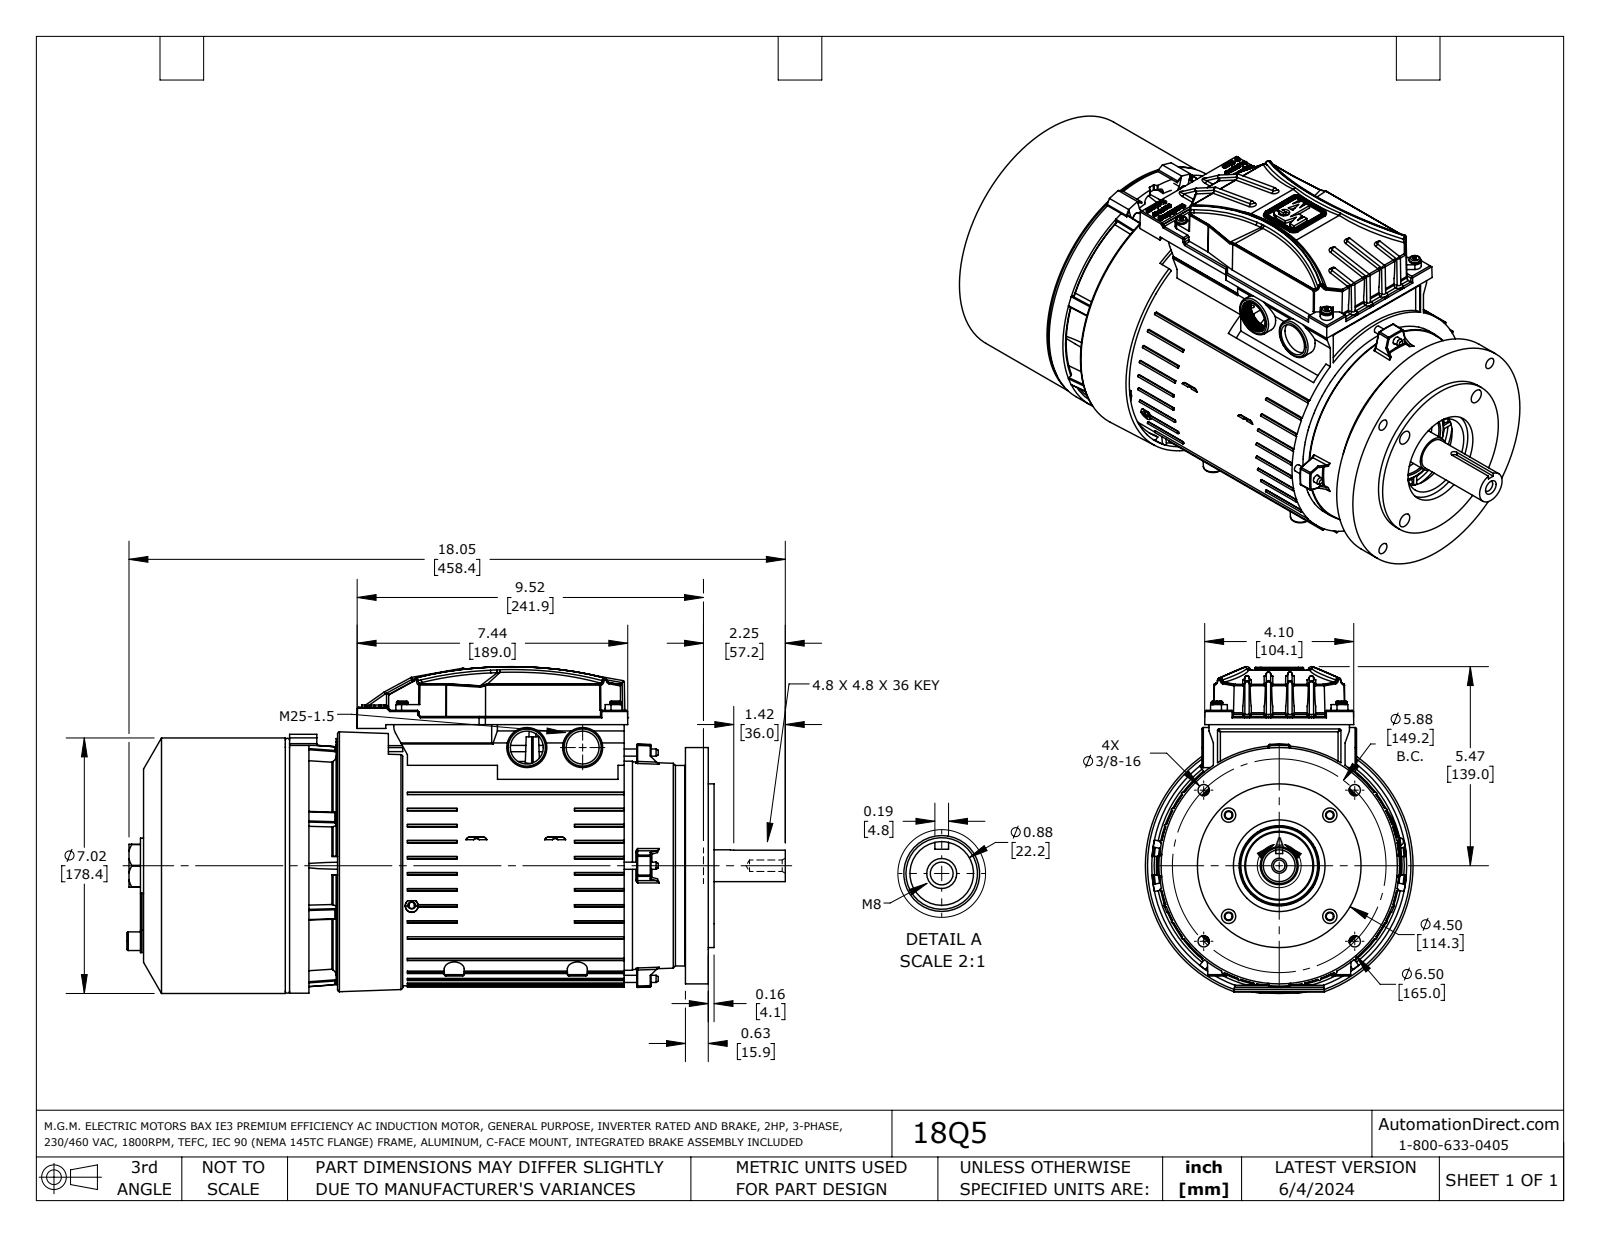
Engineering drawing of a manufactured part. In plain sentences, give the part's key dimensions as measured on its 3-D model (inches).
The part is named "18Q5". Its 3-D file was written by "SolidWorks 2021 (AUTOMOTIVE_DESIGN)". It is 14 solids with 3356 faces: 1425 planar, 768 cylindrical and 1163 other. Overall it measures 18.107 by 8.985 by 7.361 inches. Its volume is 506.6 cubic inches and its surface area 1 038 square inches. Round holes: 14 of diameter 0.13, 5 of diameter 0.098, 5 of diameter 0.236, 5 of diameter 0.315, 4 of diameter 0.15, 4 of diameter 0.177, 4 of diameter 0.197, 4 of diameter 0.313, 4 of diameter 0.394, 2 of diameter 0.118, 2 of diameter 0.906, 1 of diameter 0.276. Round bosses or shafts: 6 of diameter 0.197, 6 of diameter 0.138, 4 of diameter 0.315, 3 of diameter 0.276, 2 of diameter 1.102, 2 of diameter 0.453, 2 of diameter 0.256, 1 of diameter 7.087. Partial cylindrical surfaces (rounded edges, fillets, slot ends): 47 of radius 0.059, 32 of radius 0.008, 24 of radius 0.004, 22 of radius 0.02, 22 of radius 0.031, 20 of radius 0.024, 16 of radius 0.033, 16 of radius 0.039. The main face-to-face distances are 0.394, 14.902, 0.628, 15.529, 0.234, 15.295, 1.122, 0.787, 0.335, 1.35. The hole center spacings are 0.472, 3.536, 0.818, 0.969, 1.517, 1.669, 1.902, 1.969.
